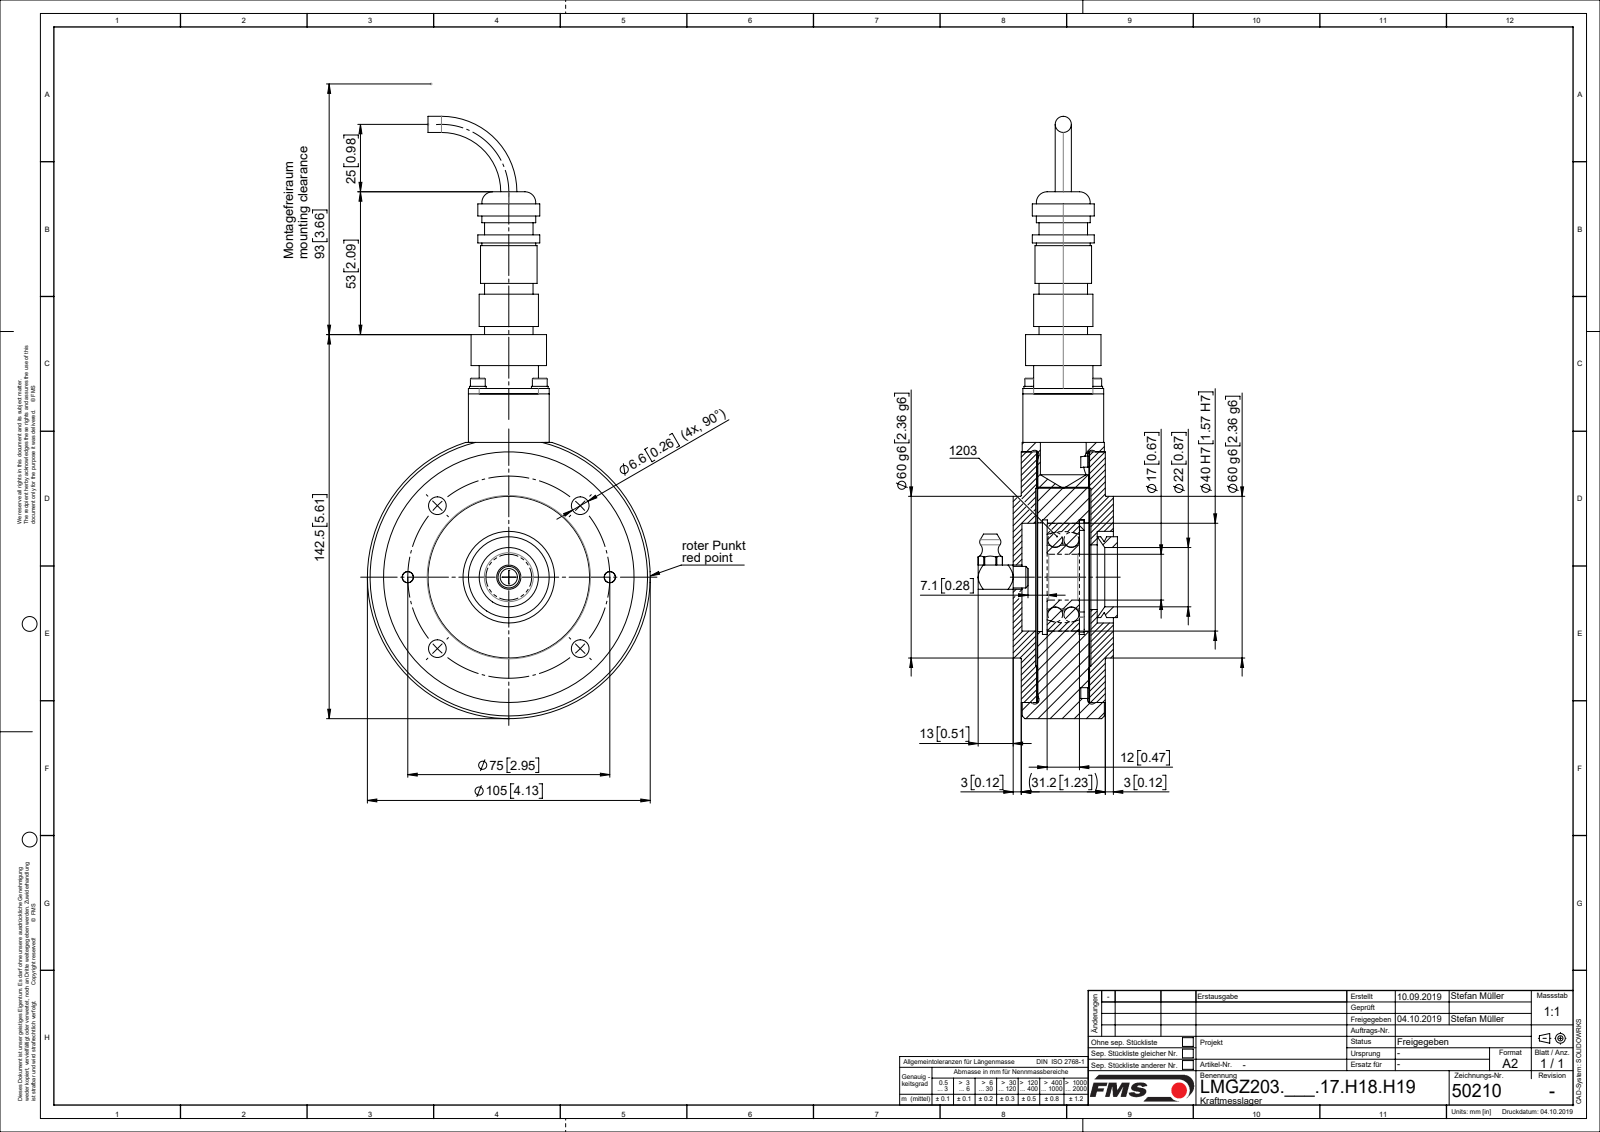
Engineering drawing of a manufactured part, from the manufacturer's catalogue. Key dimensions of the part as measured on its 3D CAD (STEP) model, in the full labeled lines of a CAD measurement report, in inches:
Part name (STEP PRODUCT): ZEICHNUNG7; L50210; L4795904; L47958(1) (+8 more)
STEP written by: Mechanical Desktop 2007 (CONFIG_CONTROL_DESIGN)
Units: inches
Bodies: 21 solids, 398 faces (111 planar, 231 cylindrical, 56 other)
Overall size (bounding box): 8.799 × 4.134 × 2.035
Volume: 18.05 in³ · Surface area: 164.1 in²
Round holes (diameter × count): ⌀0.102 ×4, ⌀0.126 ×4, ⌀0.134 ×4, ⌀0.26 ×4, ⌀0.157 ×2, ⌀0.209 ×2, ⌀0.217 ×2, ⌀0.394 ×2, ⌀0.342 ×1, ⌀0.669 ×1, ⌀0.866 ×1, ⌀0.945 ×1
Round bosses / shafts (diameter × count): ⌀0.244 ×4, ⌀0.217 ×4, ⌀0.118 ×4, ⌀0.098 ×4, ⌀0.315 ×3, ⌀0.197 ×2, ⌀4.134 ×1, ⌀3.661 ×1
Partial cylindrical surfaces — rounded edges, fillets, slot ends (radius × count): R0.157 ×4, R0.079 ×1
Main face-to-face distances: 0.758, 0.748, 0.23, 0.988, 0.24, 0.998, 0.768, 0.787, 0.118, 0.778
Hole centre spacings: 1.476, 0.906, 1.13, 2.088, 2.728, 1.281, 2.953, 2.953
